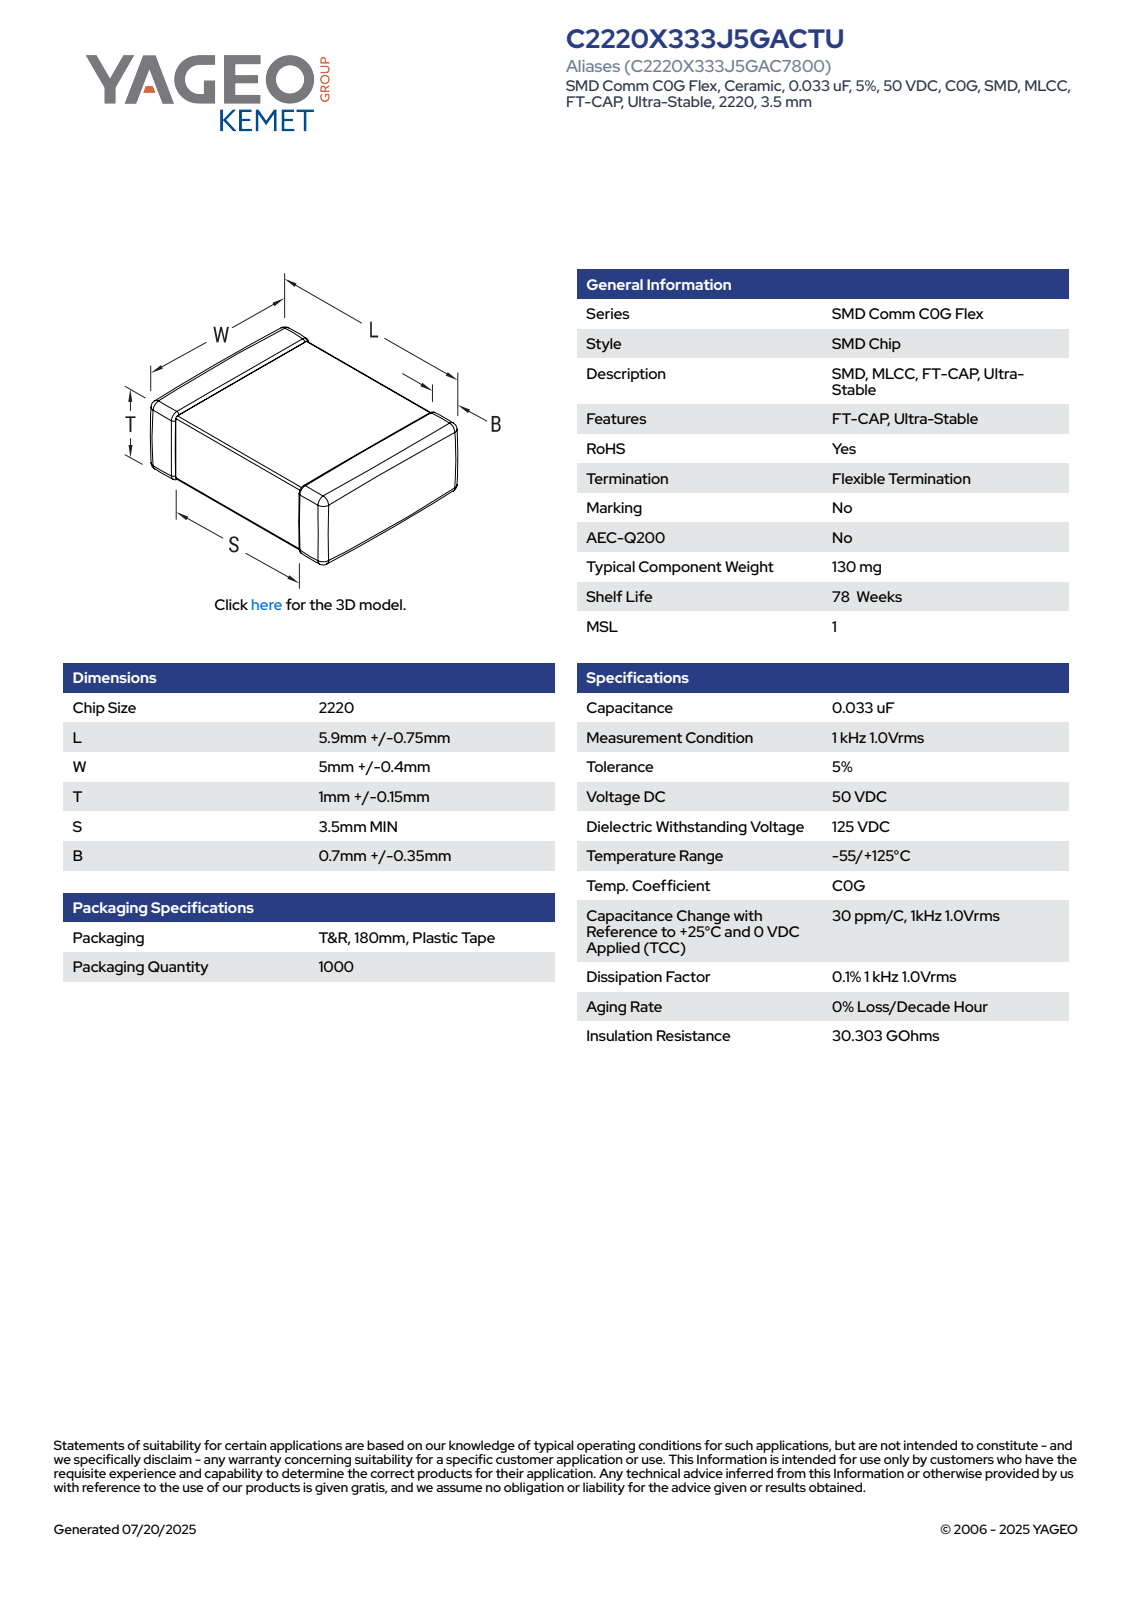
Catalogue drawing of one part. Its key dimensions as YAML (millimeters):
part_name: "CCS_CCSTD_2220_L6.65W5.4T1.15B0.7"
step_written_by: "SolidWorks 2021 (AUTOMOTIVE_DESIGN)"
units: millimeters
bodies: {solids: 4, faces: 121, planar: 71, cylindrical: 34, other: 16}
overall_size: [6.65, 5.4, 1.15]
volume: 35
surface_area: 98
partial_cylinders:
  - {radius: 0.11, count: 24}
face_to_face_distances: [0.93, 1.04, 1.15, 6.65, 5.18, 5.29, 5.4, 2.8, 3.85, 3.59]
